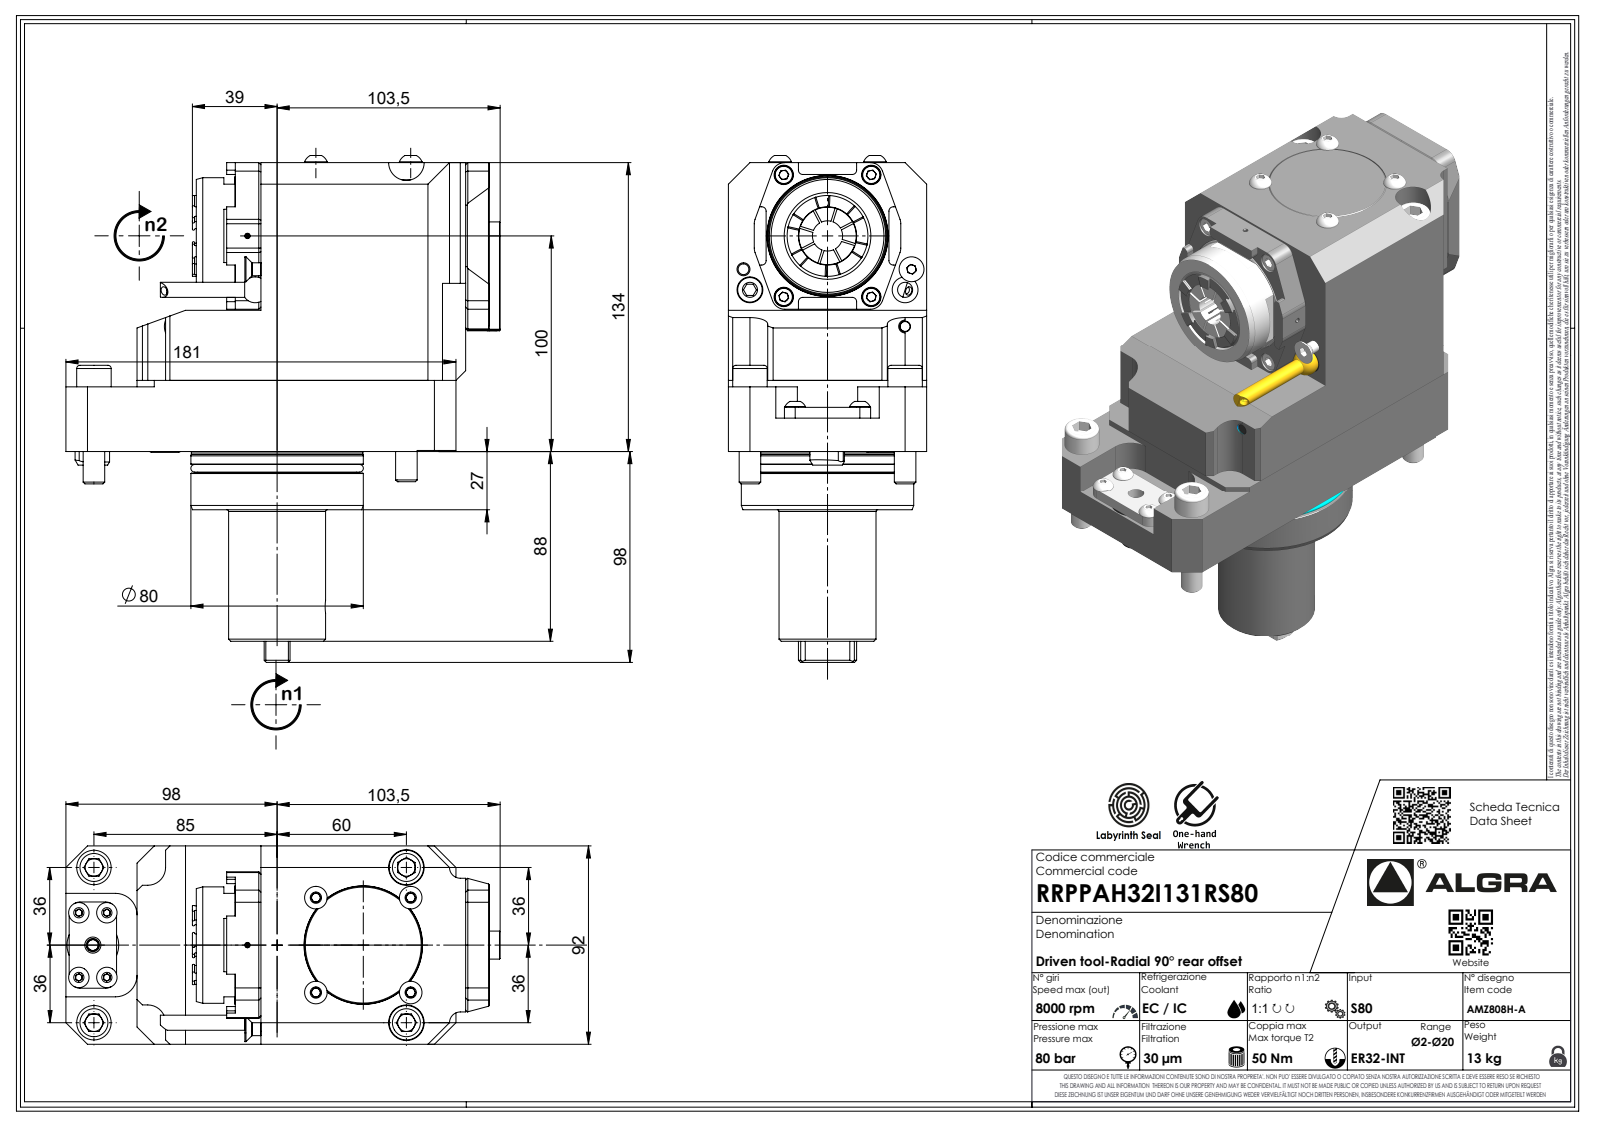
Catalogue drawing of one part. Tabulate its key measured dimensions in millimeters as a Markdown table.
| quantity | value |
| --- | --- |
| part name | RRPPAH32I131RS80 |
| STEP written by | SolidWorks 2023 (AUTOMOTIVE_DESIGN) |
| units | millimeters |
| bodies | 1 solid, 622 faces (378 planar, 83 cylindrical, 161 other) |
| overall size | 231.8 × 201 × 92 |
| volume | 1 882 000 mm³ |
| surface area | 119 843 mm² |
| round holes (diameter × count) | 2.1 × 1 |
| round bosses / shafts (diameter × count) | 80 × 1, 79.6 × 1, 73.6 × 1, 54 × 1, 45 × 1, 16 × 1, 6.37 × 1, 1.7 × 1 |
| partial cylindrical surfaces (radius × count) | 2 × 8, 6 × 8, 0.33 × 7, 0.52 × 7, 3.7 × 7, 5 × 6, 8.25 × 4, 6.5 × 2 |
| main face-to-face distances | 92, 134, 68.5, 65.5, 90.5, 15, 30, 27, 92.5, 161 |
